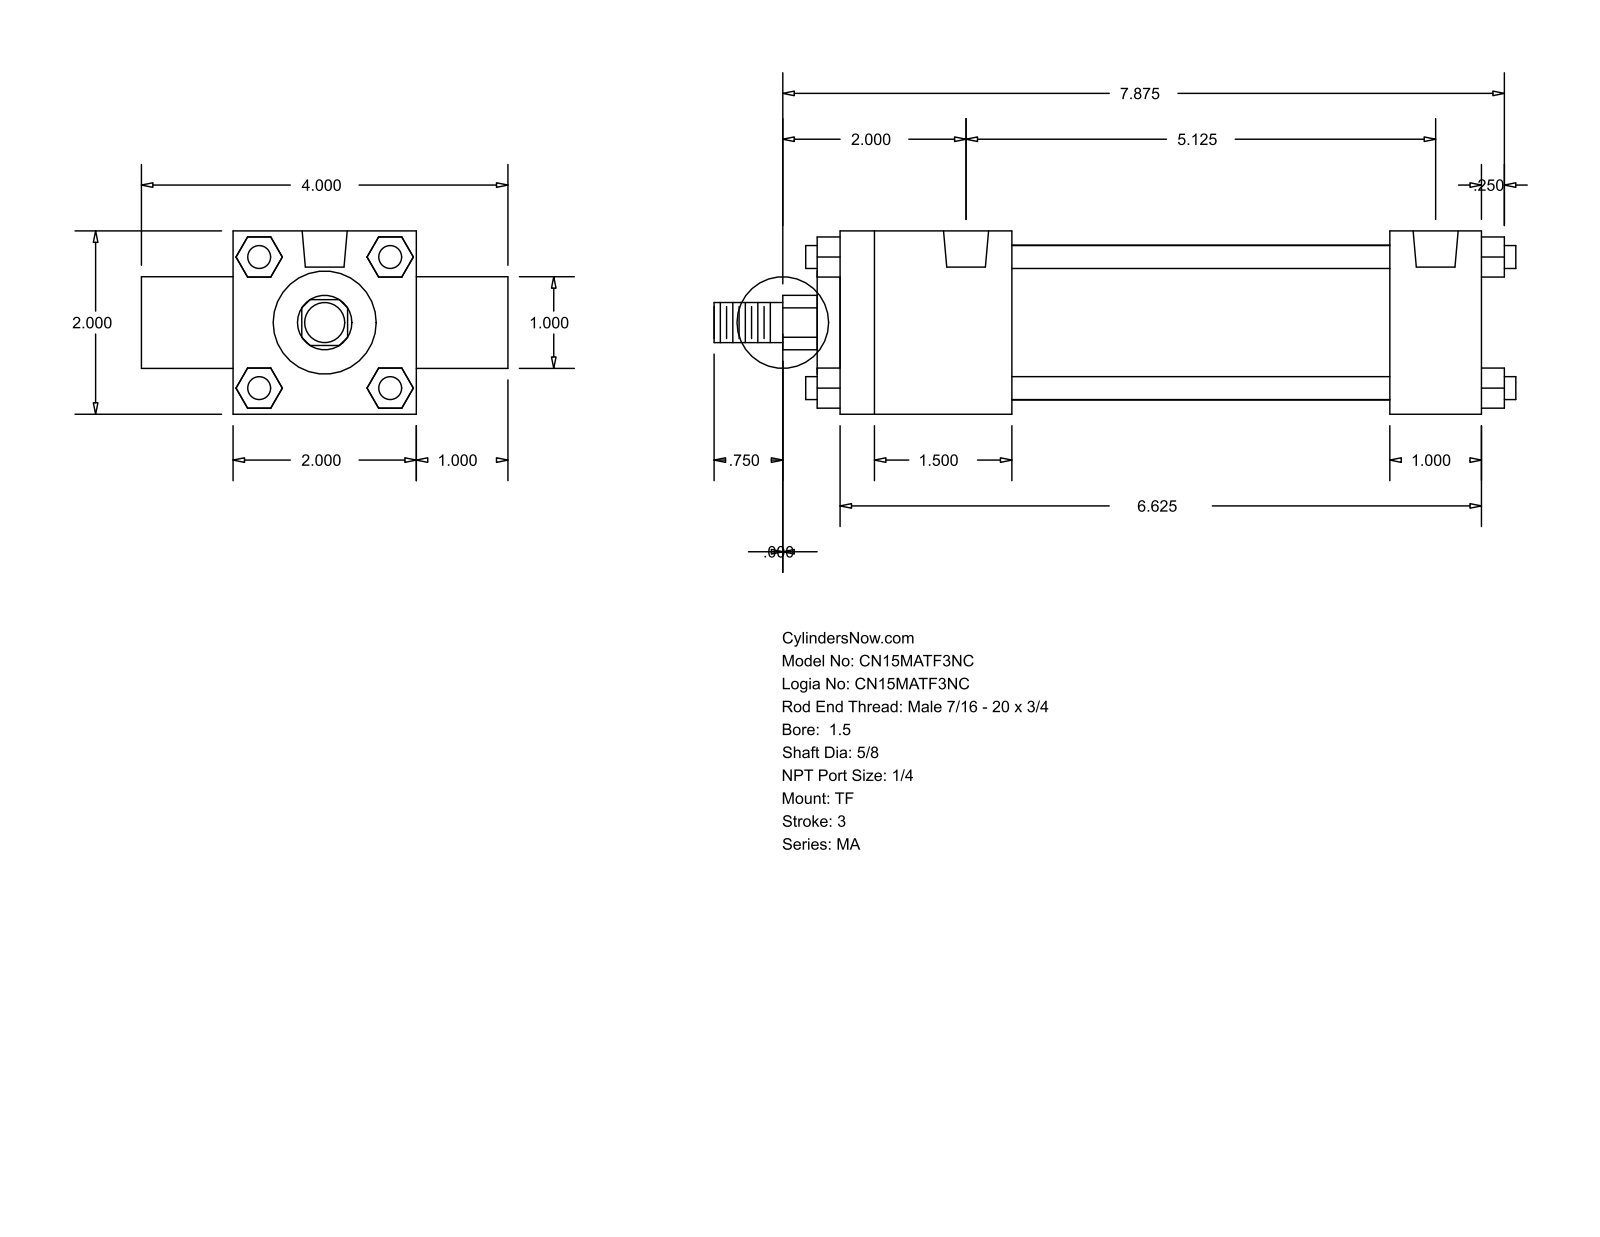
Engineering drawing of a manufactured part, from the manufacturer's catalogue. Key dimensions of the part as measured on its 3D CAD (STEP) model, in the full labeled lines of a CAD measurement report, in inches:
Part name (STEP PRODUCT): MA_TF__0150_0.625
STEP written by: GSSL Pune (CONFIG_CONTROL_DESIGN)
Units: inches
Bodies: 0 solids, 120 faces (92 planar, 28 cylindrical, 0 other)
Overall size (bounding box): 8.75 × 4 × 2
Round holes (diameter × count): ⌀0.313 ×3, ⌀0.492 ×2
Round bosses / shafts (diameter × count): ⌀0.25 ×4, ⌀1.69 ×1, ⌀1.125 ×1, ⌀1 ×1, ⌀0.625 ×1, ⌀0.437 ×1
Partial cylindrical surfaces — rounded edges, fillets, slot ends (radius × count): R0.297 ×1
Main face-to-face distances: 2, 1, 7, 0.25, 7.25, 3, 1.875, 6, 4.125, 5.125
Hole centre spacings: 5.125
